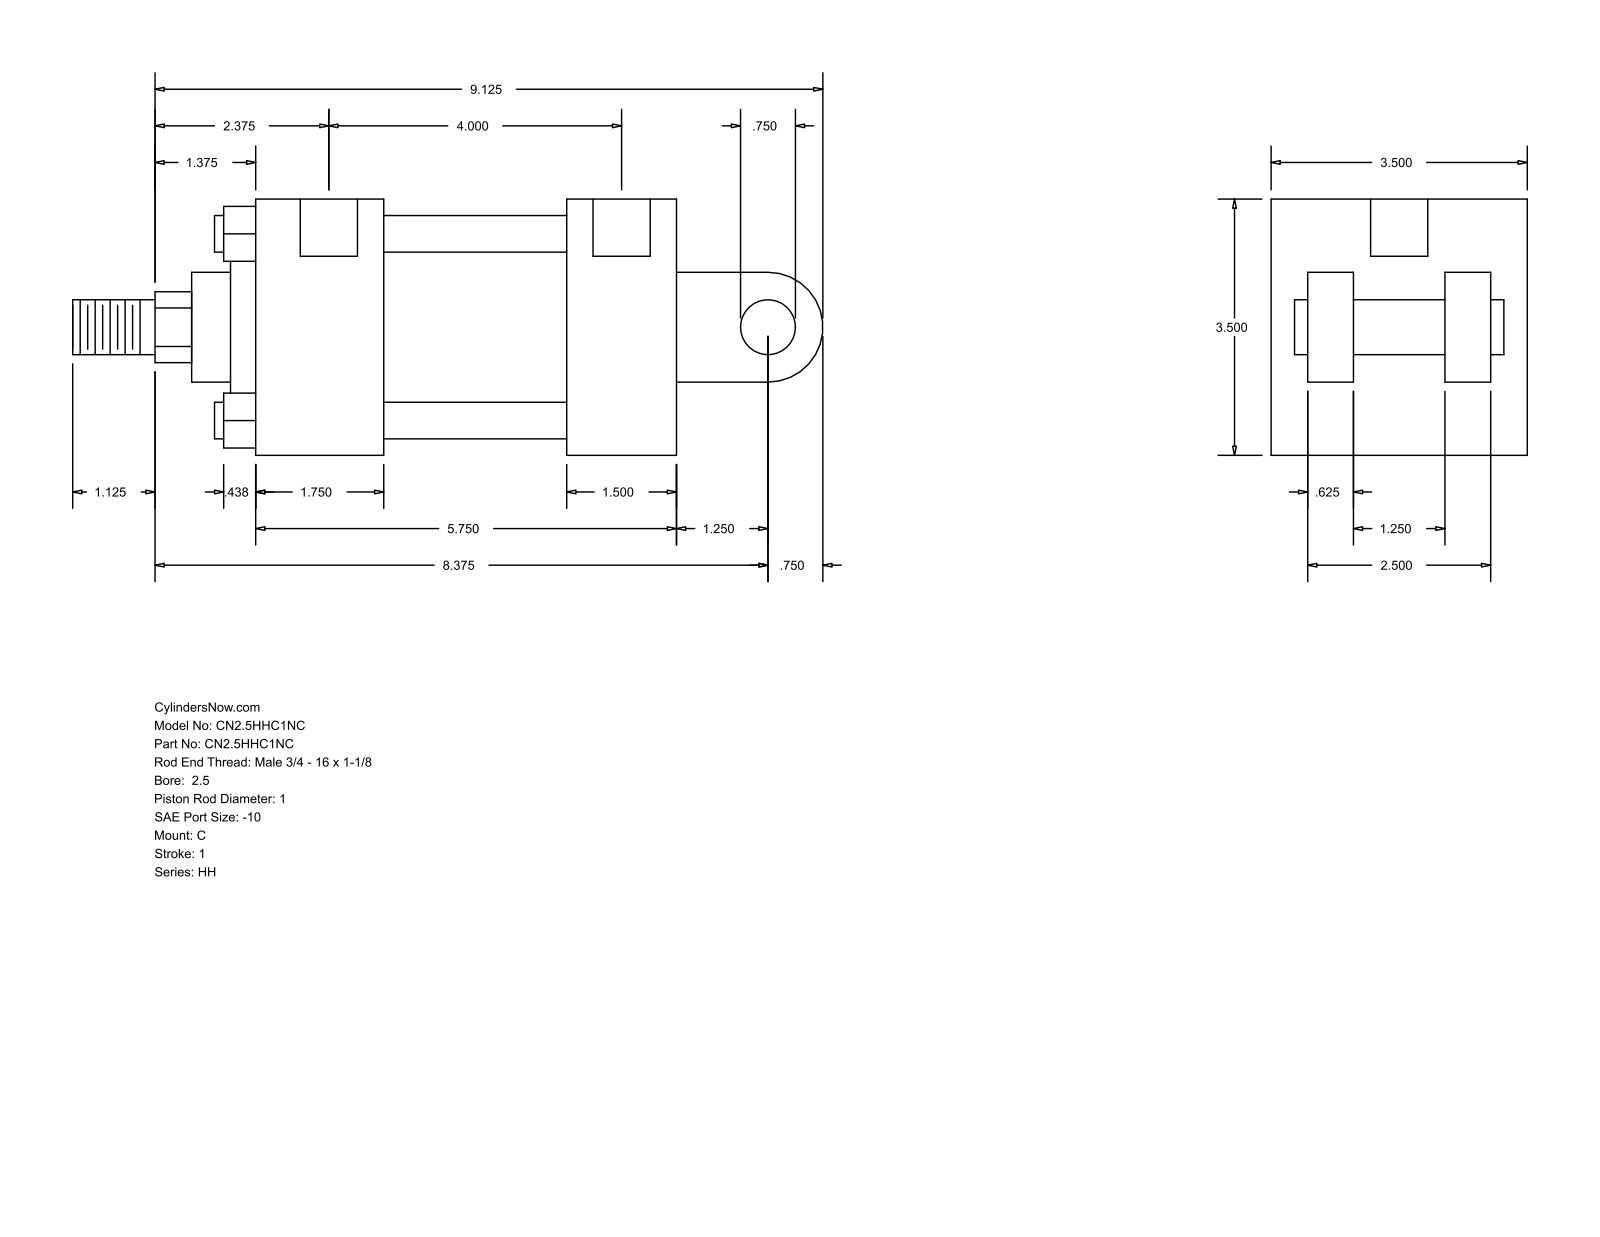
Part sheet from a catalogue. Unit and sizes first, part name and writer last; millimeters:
Units: millimetres
Overall size (bounding box): 260.35 × 88.9 × 88.9
Round holes (diameter × count): ⌀5.56 ×4, ⌀19.84 ×2
Round bosses / shafts (diameter × count): ⌀12.7 ×4, ⌀19.05 ×2, ⌀73.03 ×1, ⌀60.33 ×1, ⌀38.1 ×1, ⌀25.4 ×1
Partial cylindrical surfaces — rounded edges, fillets, slot ends (radius × count): R12.29 ×1, R19.05 ×1
Main face-to-face distances: 88.9, 63.5, 146.05, 107.96, 38.09, 44.46, 101.59, 12.7, 28.57, 76.2
Hole centre spacings: 104.77, 1.58, 1.59, 101.6, 103.18, 103.19
Bodies: 0 solids, 101 faces (71 planar, 30 cylindrical, 0 other)
Part name (STEP PRODUCT): HH_C__0250_1
STEP written by: GSSL Pune (CONFIG_CONTROL_DESIGN)
